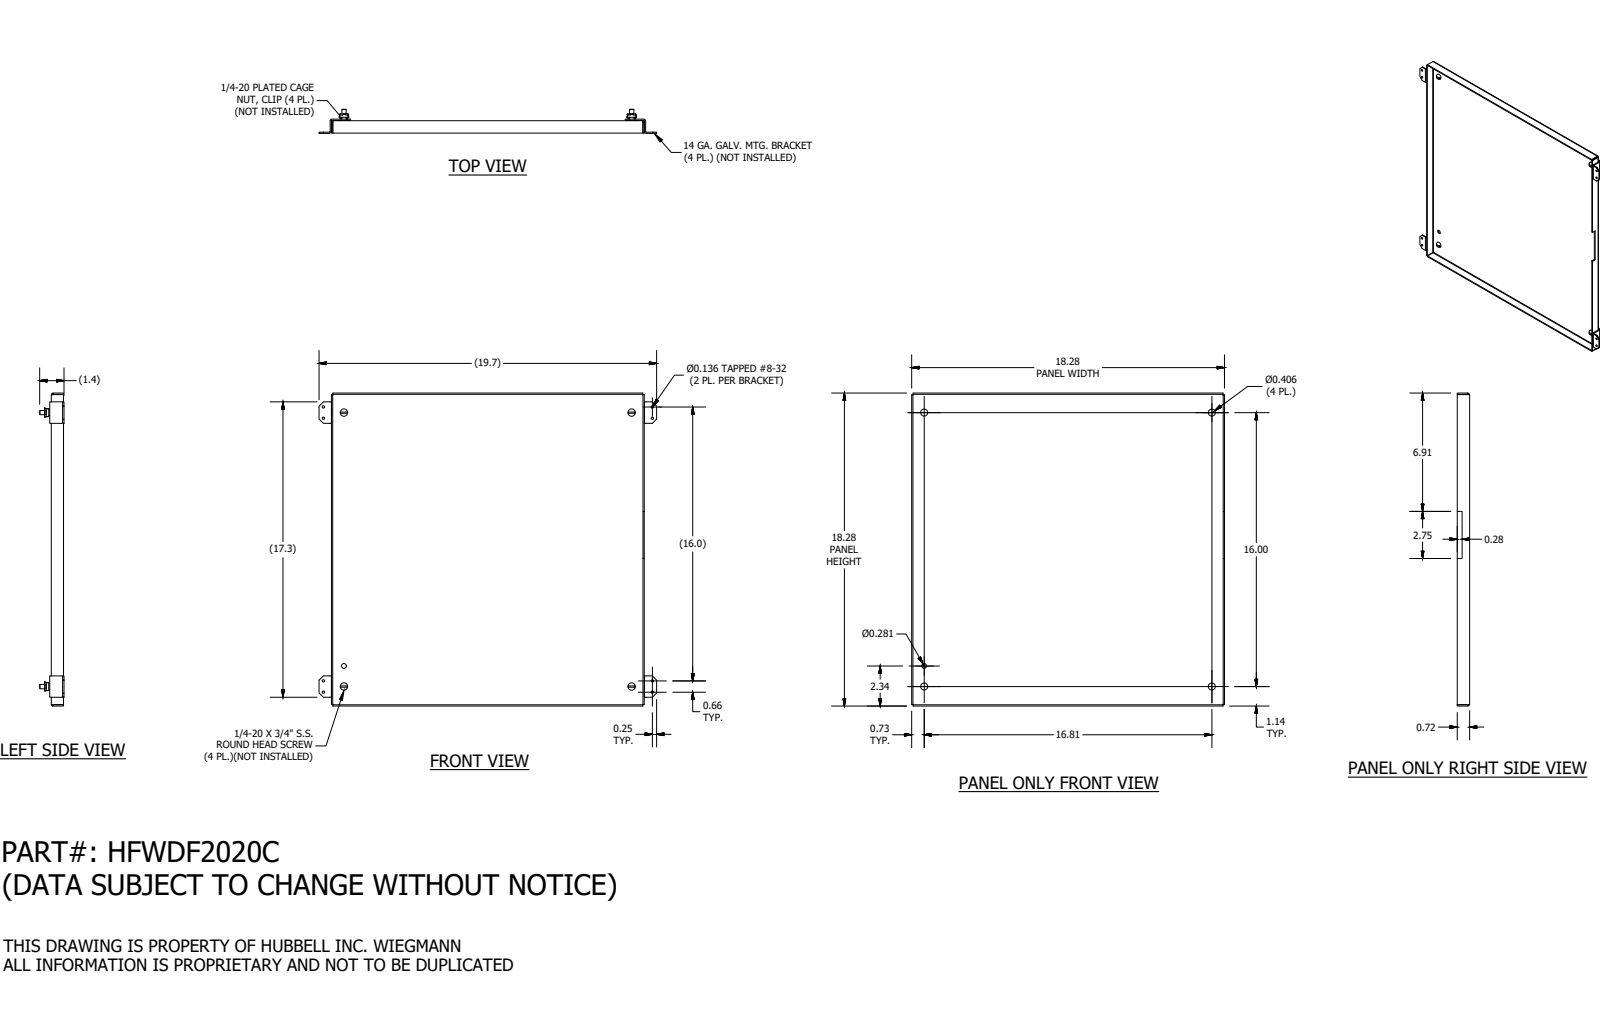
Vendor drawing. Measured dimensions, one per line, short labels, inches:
name: HFWDF2020C
written by: SolidWorks 2023 (AUTOMOTIVE_DESIGN)
unit: in
bodies: 13 solids, 595 faces (418 planar, 161 cylindrical, 16 other)
size: 19.726 × 18.281 × 1.415
volume: 29.17 in³; area: 798.6 in²
holes: 8× ⌀0.136, 4× ⌀0.185, 4× ⌀0.328, 4× ⌀0.406, 1× ⌀0.281
bosses: 4× ⌀0.25
rounds: 20× R0.025, 16× R0.021, 12× R0.045, 8× R0.031, 8× R0.105, 4× R0.021
face distances: 0.074, 18.207, 18.281, 18.133, 0.094, 0.078, 18.285, 0.759, 0.665, 0.719
hole spacings: 1.251, 18.023, 16, 0.66, 15.717, 16.374, 19.227, 19.238
